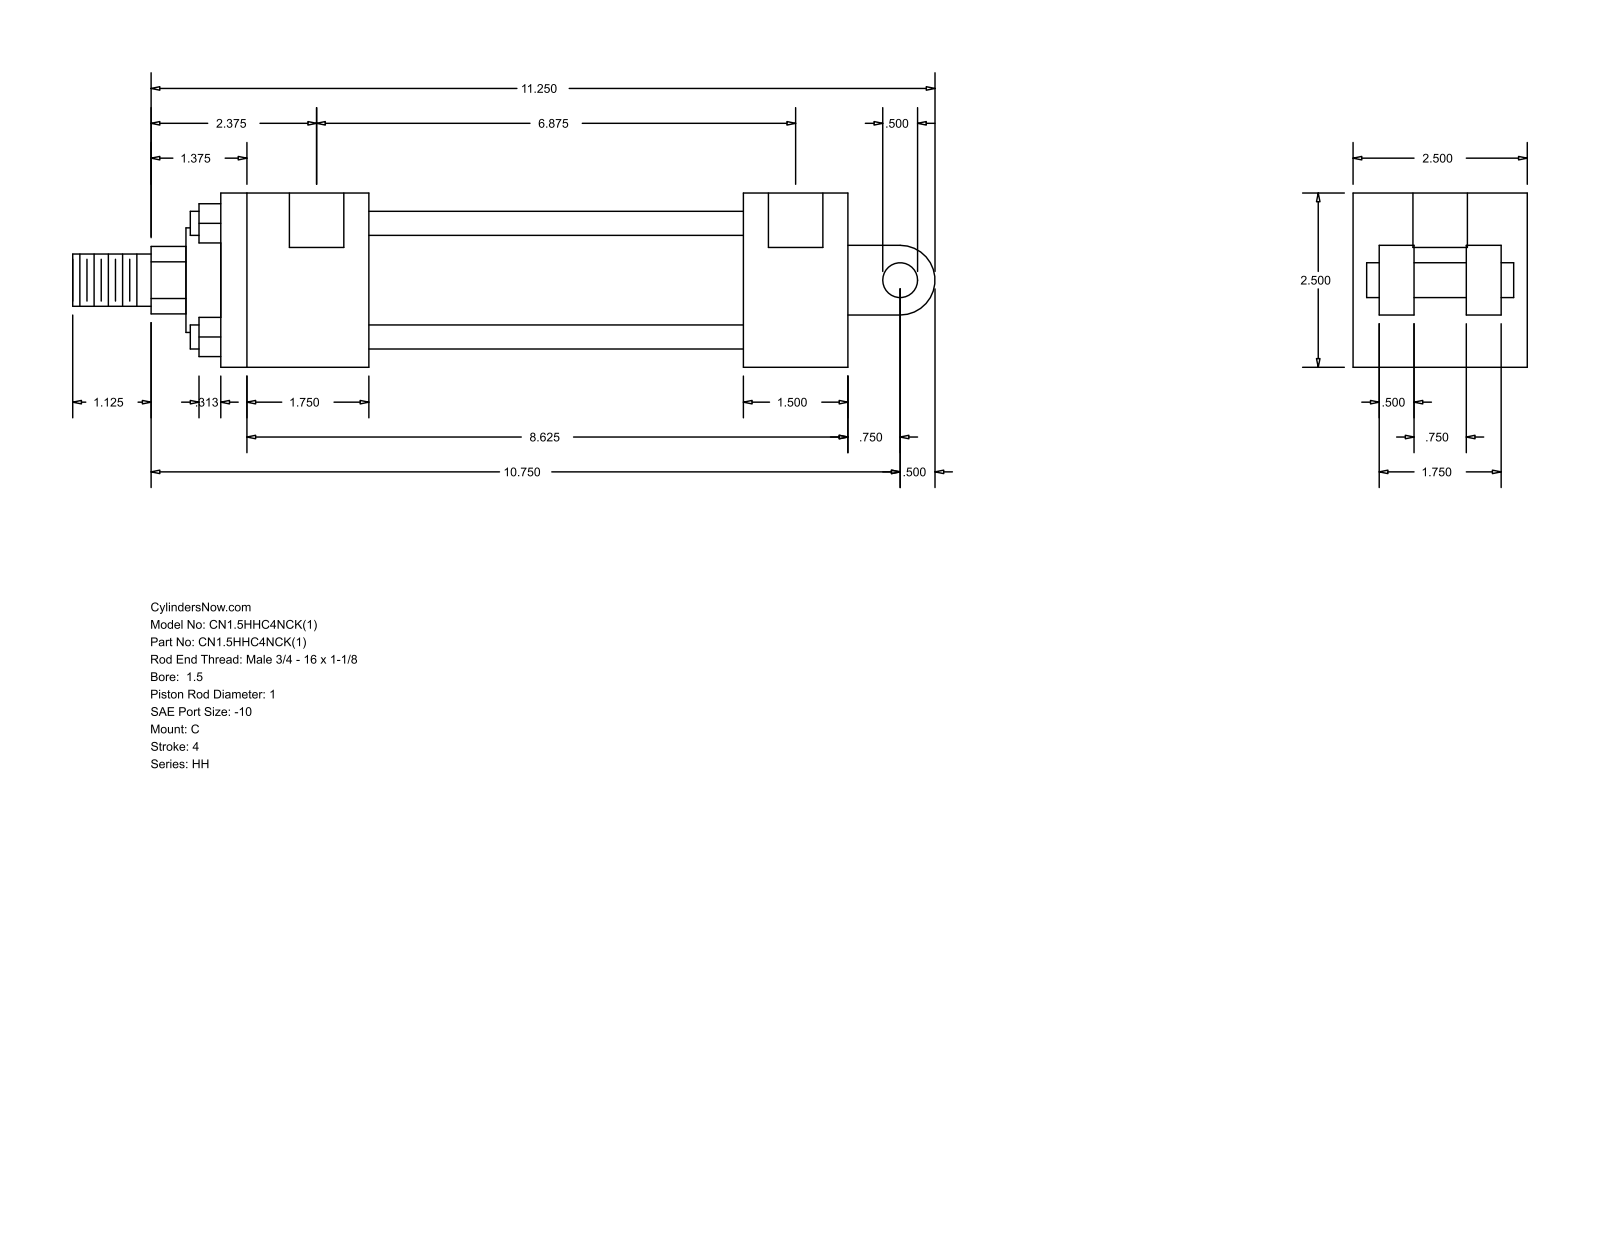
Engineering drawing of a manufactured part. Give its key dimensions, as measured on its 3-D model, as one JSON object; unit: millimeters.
{"part_name": "HH_C__0150_1", "step_written_by": "GSSL Pune (CONFIG_CONTROL_DESIGN)", "units": "millimeters", "bodies": {"solids": 0, "faces": 99, "planar": 70, "cylindrical": 29, "other": 0}, "overall_size": [314.32, 63.5, 63.5], "round_holes": [[5.56, 4], [19.84, 2]], "round_bosses_or_shafts": [[8.76, 4], [44.45, 1], [38.1, 1], [25.4, 1], [19.05, 1], [12.7, 1]], "partial_cylinders_radius": [[12.29, 1], [12.7, 1]], "face_to_face_distances": [63.5, 53.98, 38.1, 136.52, 174.62, 190.5, 228.6, 12.7, 22.22, 41.28], "hole_center_spacings": [1.59, 176.21, 177.8, 174.62]}
